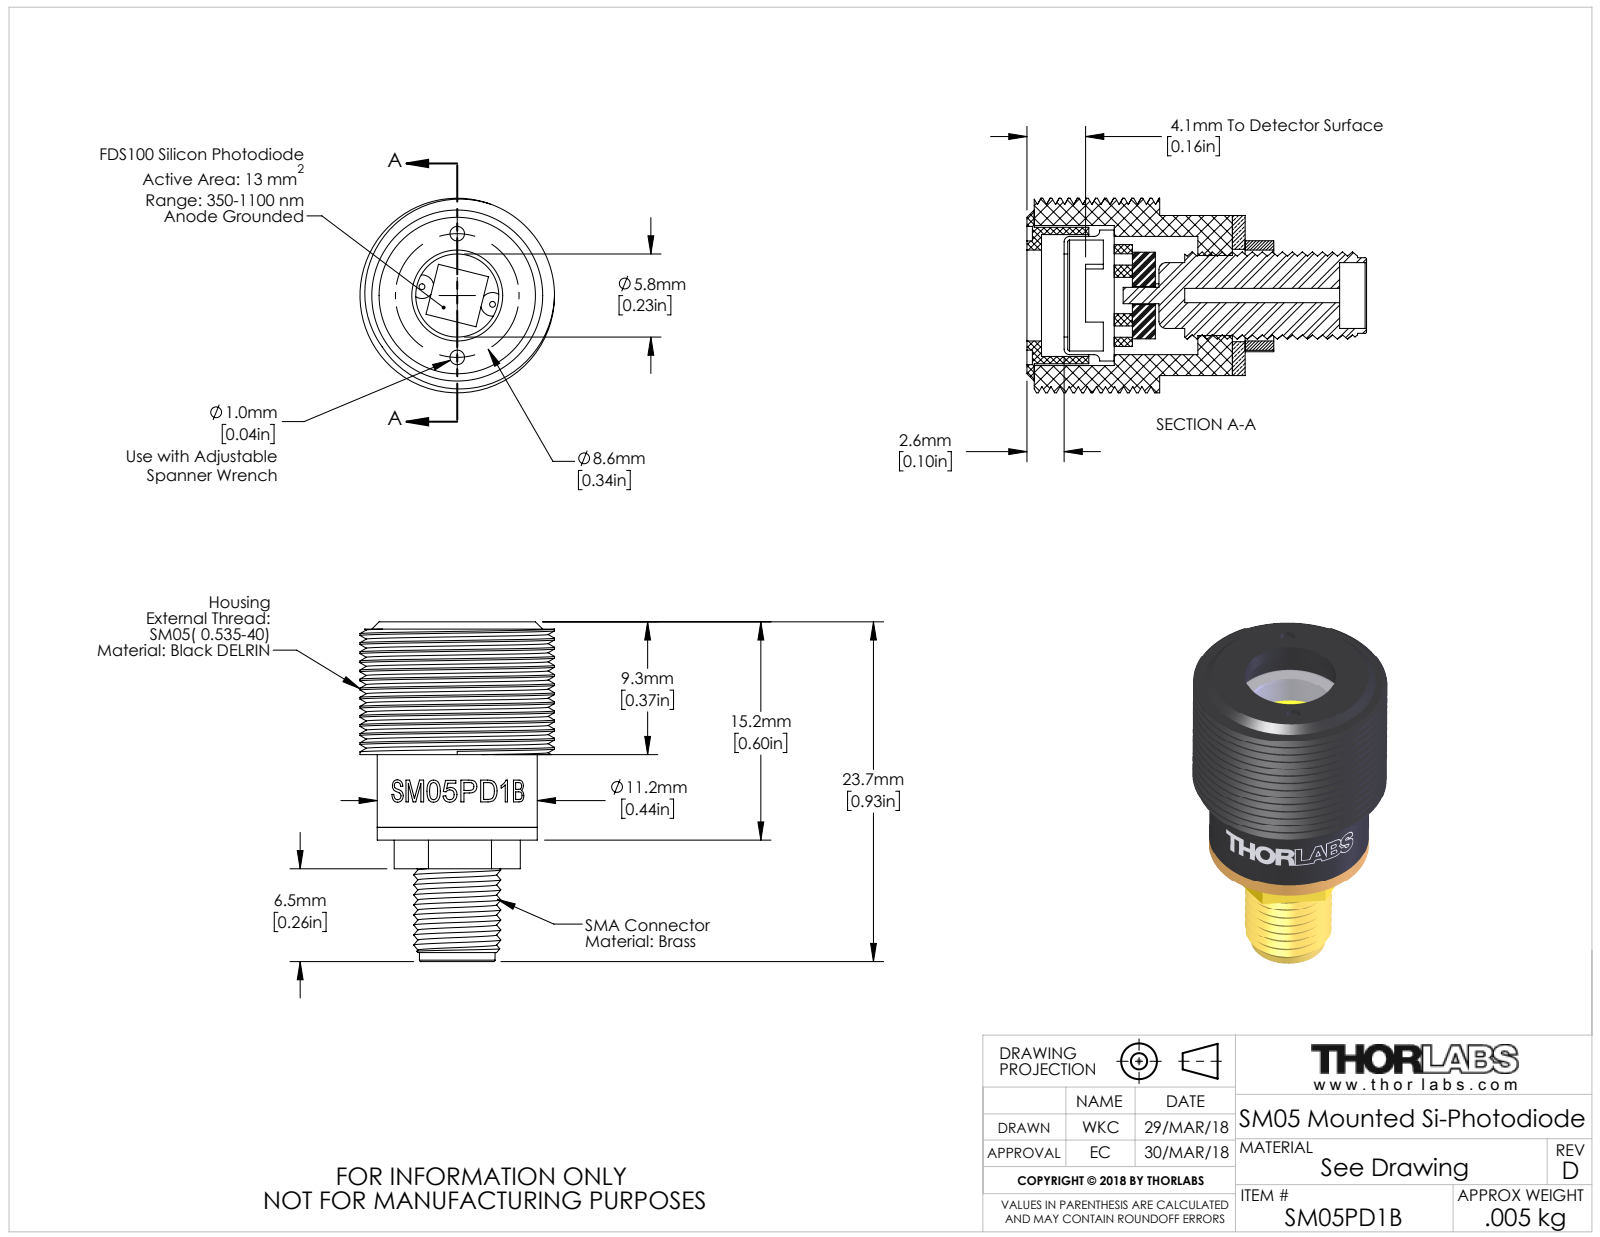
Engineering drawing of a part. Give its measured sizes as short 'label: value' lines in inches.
name: 8771-E0W
written by: SolidWorks 2016 (AUTOMOTIVE_DESIGN)
unit: in
bodies: 6 solids, 126 faces (51 planar, 59 cylindrical, 16 other)
size: 0.924 × 0.535 × 0.535
volume: 0.09 in³; area: 4.407 in²
holes: 2× ⌀0.04, 2× ⌀0.065, 1× ⌀0.039, 1× ⌀0.181, 1× ⌀0.22, 1× ⌀0.228, 1× ⌀0.25, 1× ⌀0.254, 1× ⌀0.305, 1× ⌀0.325, 1× ⌀0.335, 1× ⌀0.385
bosses: 3× ⌀0.016, 1× ⌀0.535, 1× ⌀0.44, 1× ⌀0.375, 1× ⌀0.36, 1× ⌀0.325, 1× ⌀0.208, 1× ⌀0.045
rounds: 4× R0.005
face distances: 0.335, 0.02, 0.035, 0.37, 0.58, 0.545, 0.21, 0.6, 0.565, 0.23
hole spacings: 0.1, 0.123, 0.17, 0.25, 0.2, 0.34
